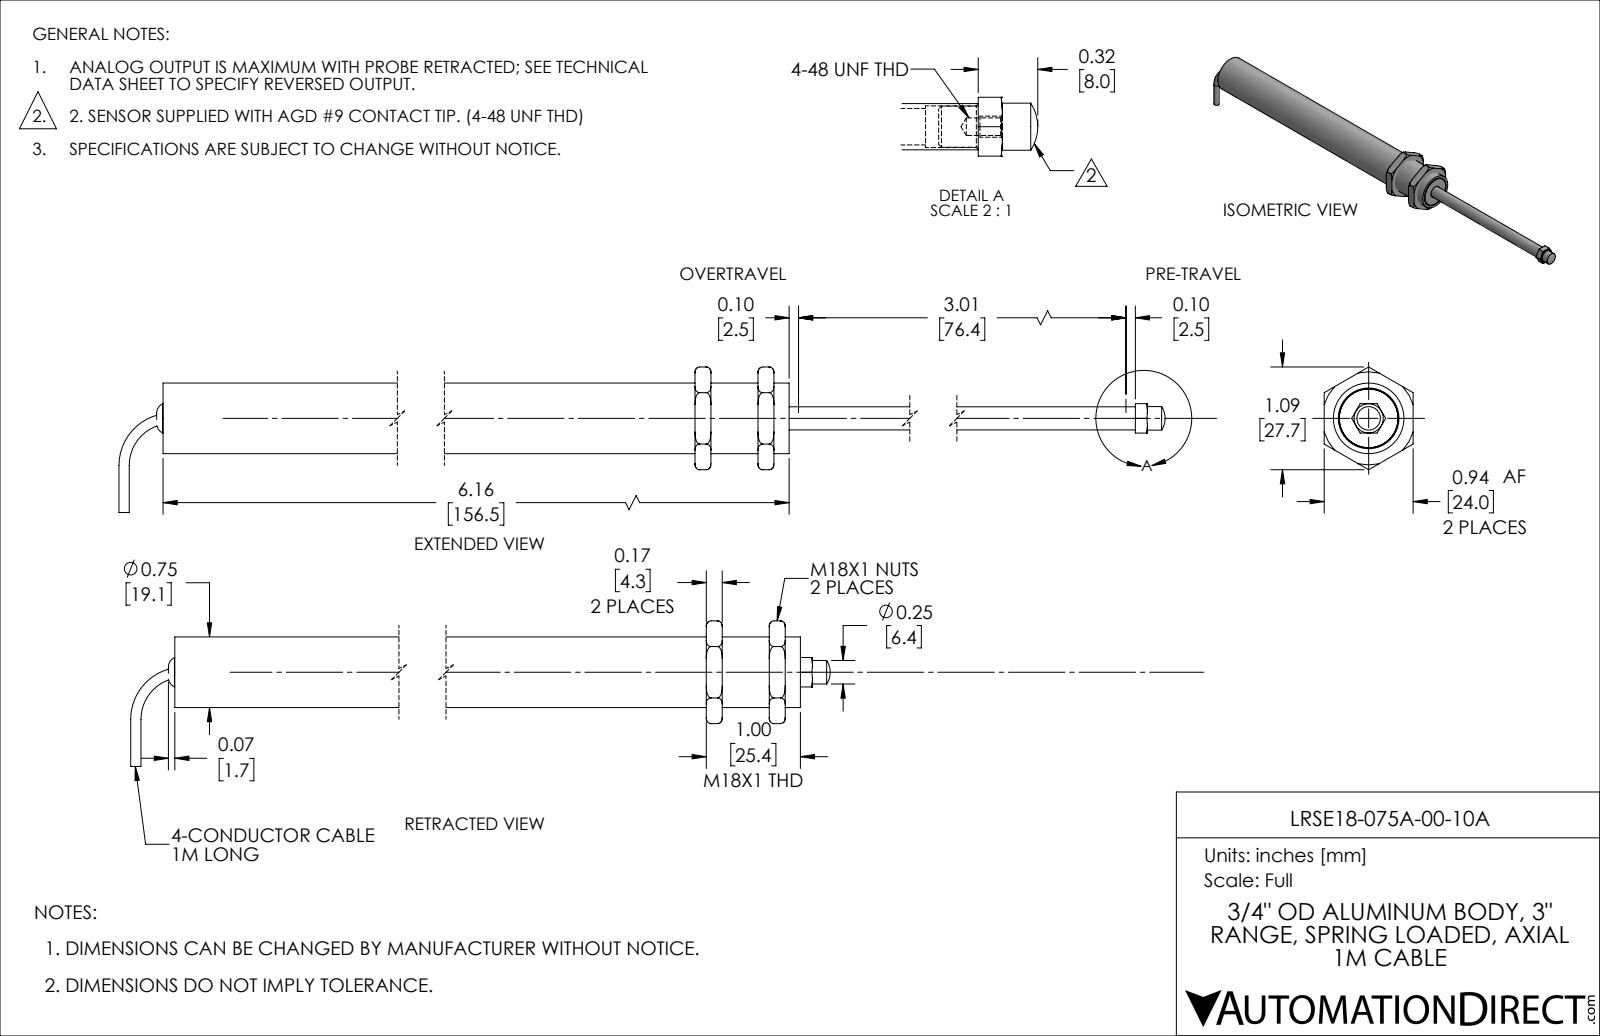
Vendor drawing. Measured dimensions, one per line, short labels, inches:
name: LRSE18-075A-00-10A
written by: SolidWorks 2019 (AUTOMOTIVE_DESIGN)
unit: in
bodies: 12 solids, 126 faces (52 planar, 29 cylindrical, 45 other)
size: 6.945 × 1.546 × 0.945
volume: 1.277 in³; area: 39 in²
holes: 1× ⌀0.093, 1× ⌀0.109, 1× ⌀0.188, 1× ⌀0.261, 1× ⌀0.307, 1× ⌀0.5, 1× ⌀0.566, 1× ⌀0.62, 1× ⌀0.625, 1× ⌀0.65, 1× ⌀0.665, 1× ⌀0.71
bosses: 1× ⌀0.75, 1× ⌀0.7, 1× ⌀0.685, 1× ⌀0.656, 1× ⌀0.624, 1× ⌀0.25, 1× ⌀0.218, 1× ⌀0.112
rounds: 1× R0.322
face distances: 0.669, 0.169, 0.945, 5.524, 5.193, 0.331, 4.524, 1, 4.693, 5.363
